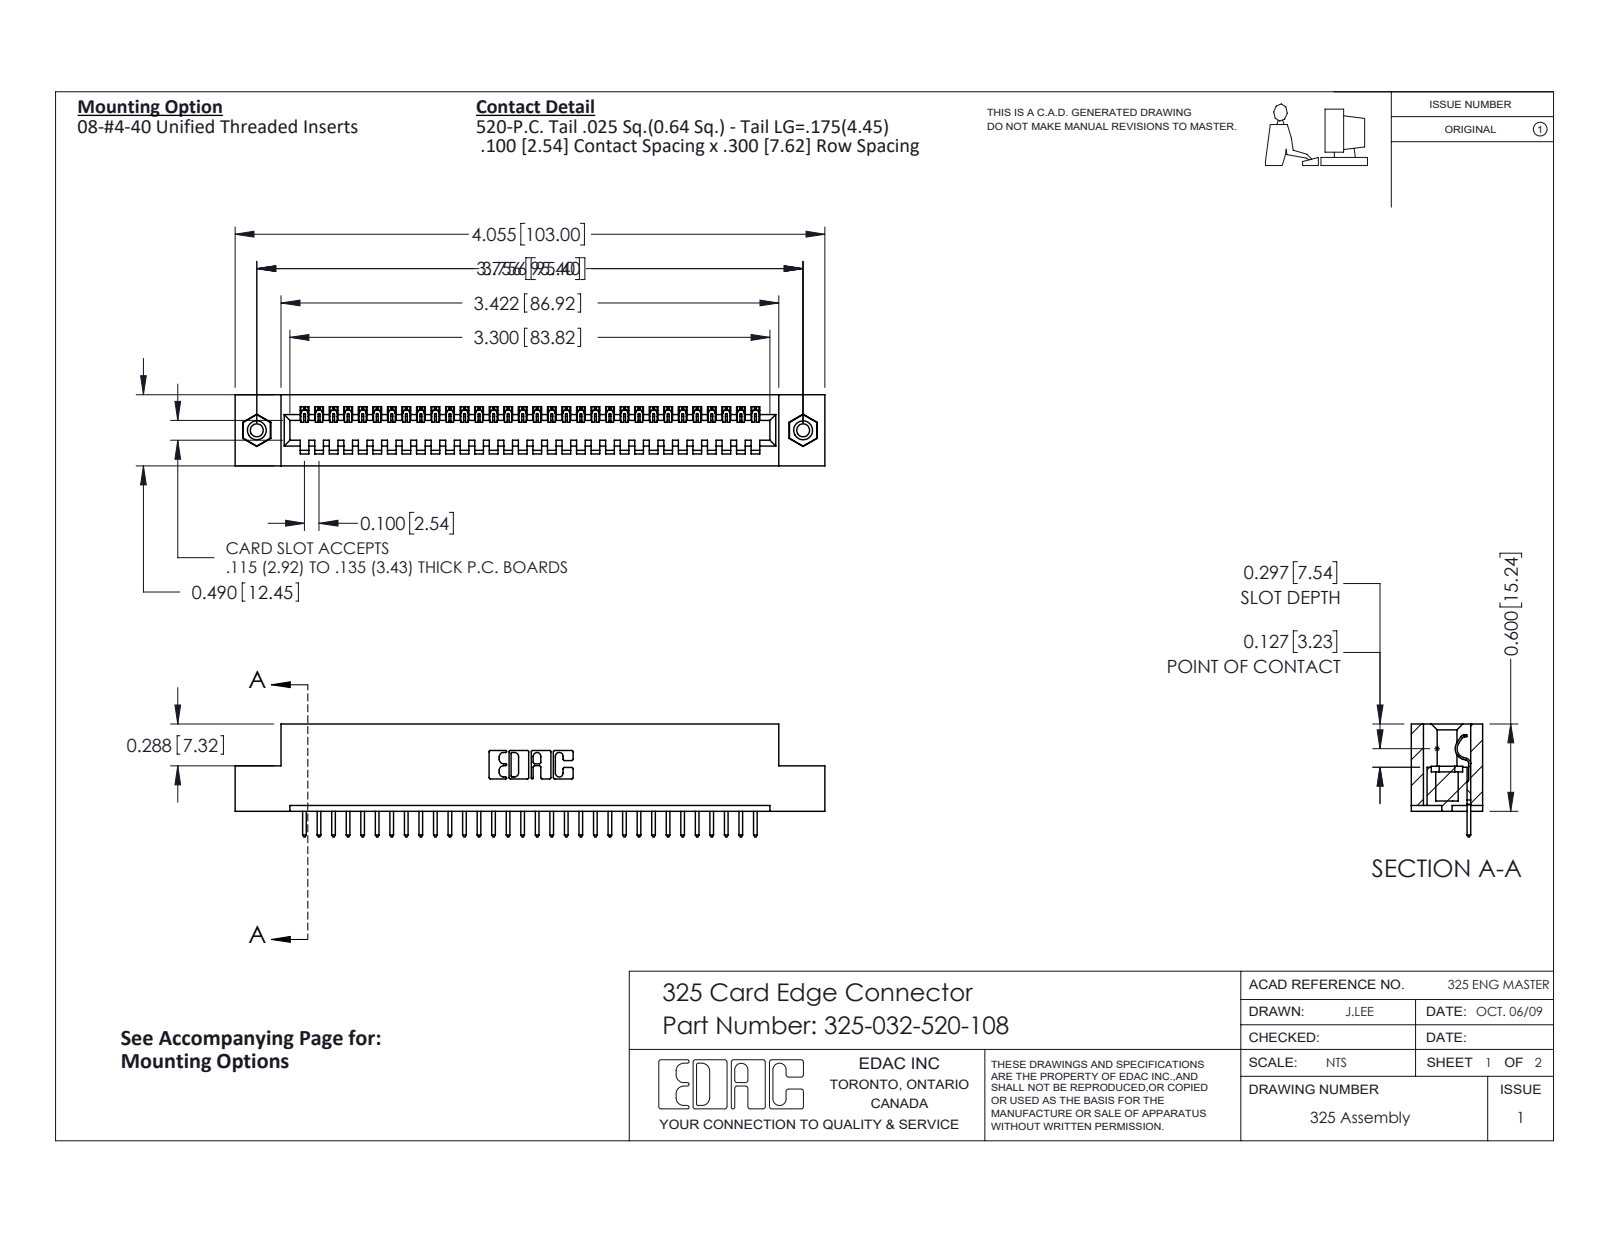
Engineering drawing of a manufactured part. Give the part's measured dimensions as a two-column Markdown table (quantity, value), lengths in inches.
| quantity | value |
| --- | --- |
| part name | 325 Part_TI; 325-292-001_325-293-120; 325-032-520-108; 345-250-001_345-250-003-102 |
| STEP written by | SolidWorks 2016 (CONFIG_CONTROL_DESIGN) |
| units | inches |
| bodies | 35 solids, 2030 faces (1446 planar, 568 cylindrical, 16 other) |
| overall size | 4.055 × 0.775 × 0.49 |
| volume | 0.788 in³ |
| surface area | 21.1 in² |
| round holes (diameter × count) | 0.089 × 2, 0.125 × 2, 0.16 × 2 |
| round bosses / shafts (diameter × count) | 0.155 × 2 |
| partial cylindrical surfaces (radius × count) | 0.006 × 64, 0.01 × 64, 0.01 × 22, 0.007 × 6, 0.031 × 6, 0.026 × 3, 0.014 × 1, 0.022 × 1 |
| main face-to-face distances | 0.083, 0.407, 0.49, 0.3, 0.107, 0.383, 0.025, 0.325, 0.04, 0.1 |
| hole center spacings | 3.756 |
